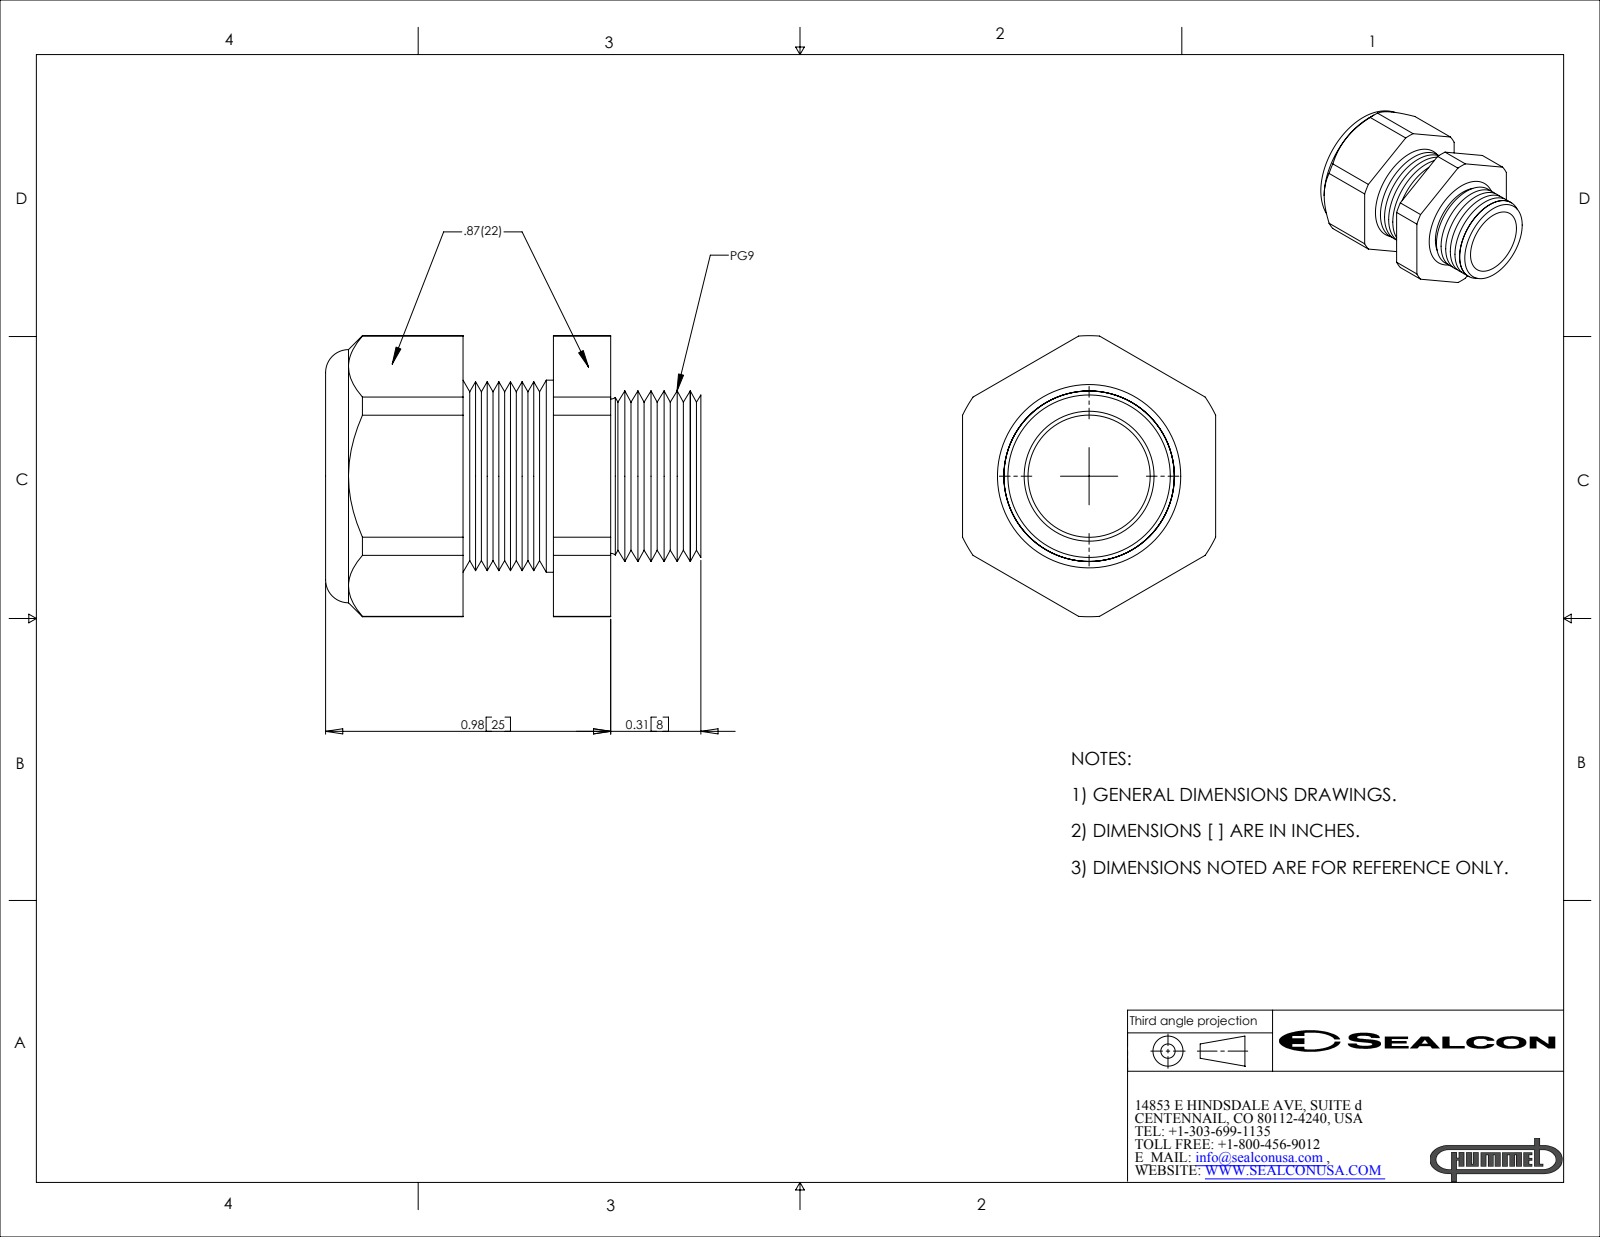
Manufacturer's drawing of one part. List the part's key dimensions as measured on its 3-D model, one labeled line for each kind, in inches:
Part name (STEP PRODUCT): CD09GA-BK
STEP written by: SolidWorks 2007 (CONFIG_CONTROL_DESIGN)
Units: inches
Bodies: 2 solids, 116 faces (20 planar, 22 cylindrical, 74 other)
Overall size (bounding box): 1.29 × 0.966 × 0.87
Volume: 0.404 in³ · Surface area: 9.399 in²
Round holes (diameter × count): ⌀0.42 ×1, ⌀0.6 ×1
Round bosses / shafts (diameter × count): ⌀0.66 ×1
Partial cylindrical surfaces — rounded edges, fillets, slot ends (radius × count): R0.483 ×1
Main face-to-face distances: 0.87, 0.508, 0.311, 0.197, 0.472, 0.783, 0.98, 0.03, 0.442, 0.753
